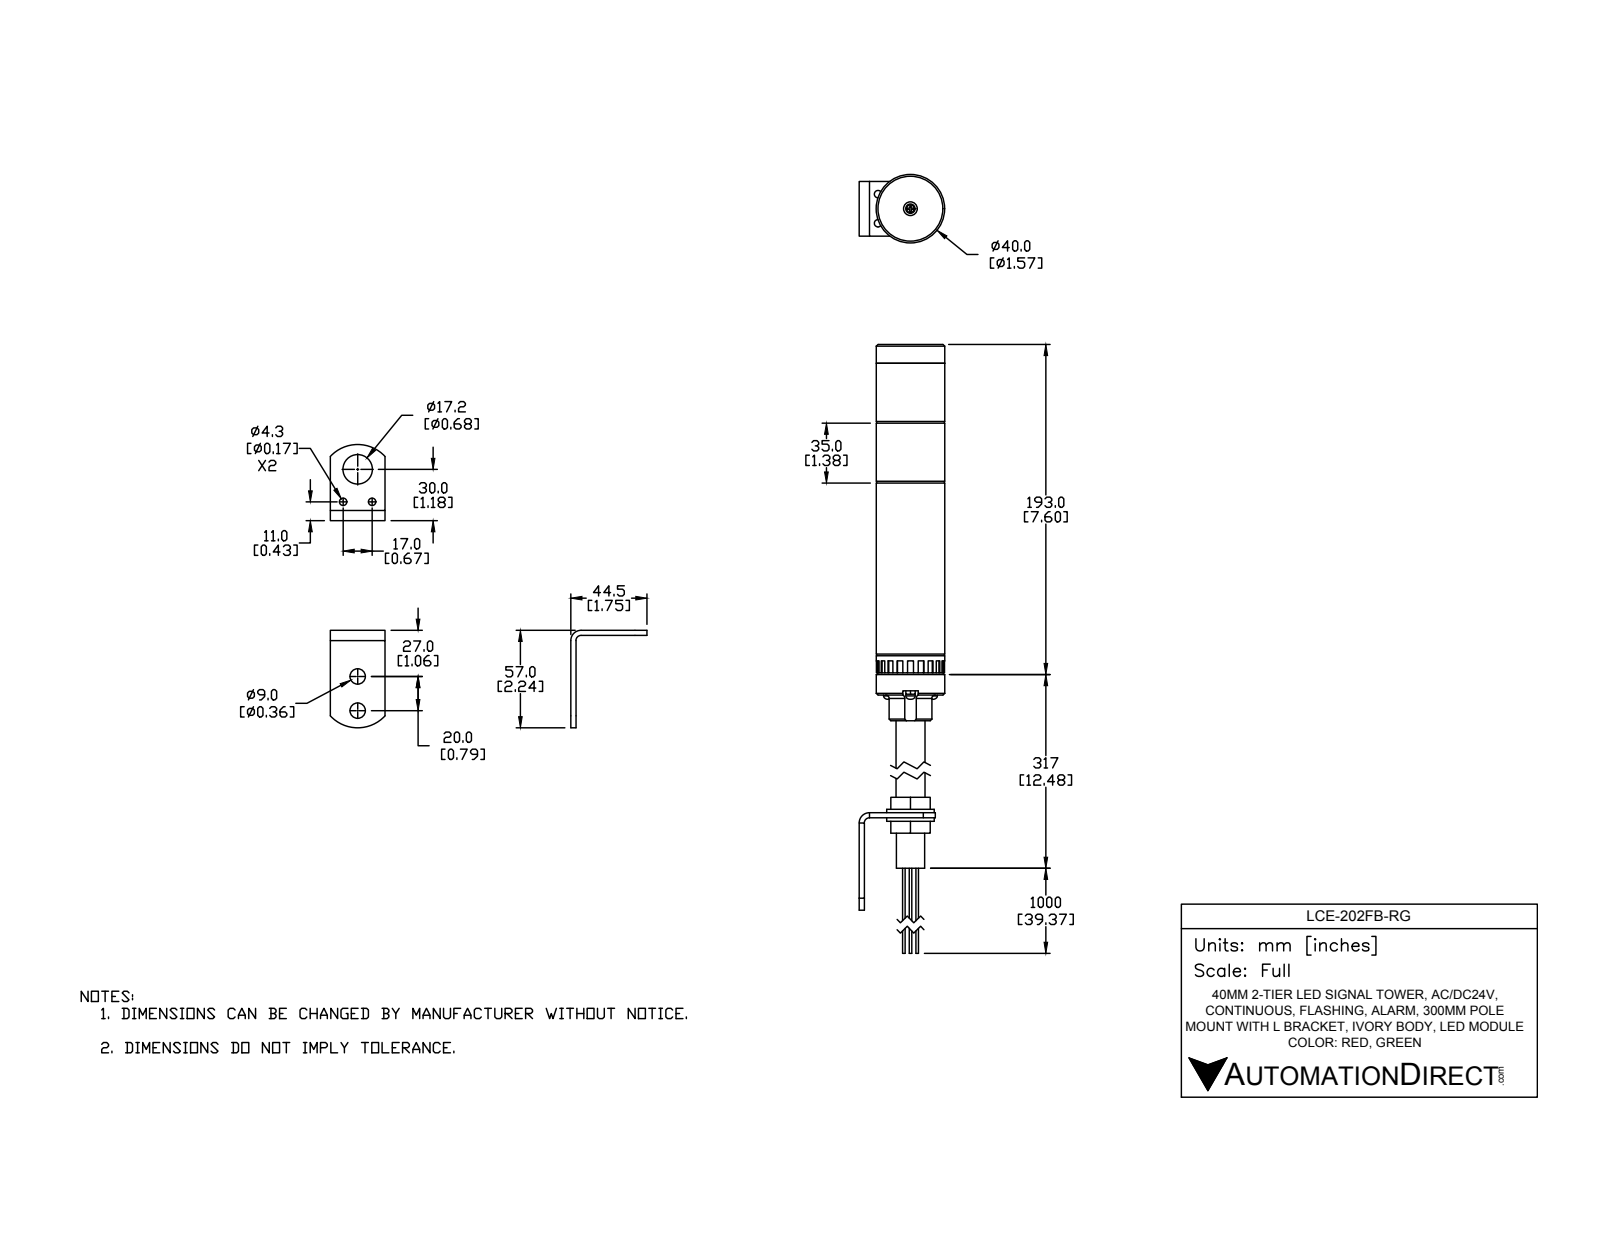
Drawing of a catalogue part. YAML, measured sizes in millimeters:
part_name: "LCE-202FB-RG"
step_written_by: "SolidWorks 2016 (AUTOMOTIVE_DESIGN)"
units: millimeters
bodies: {solids: 33, faces: 377, planar: 241, cylindrical: 116, other: 20}
overall_size: [593, 50, 40]
volume: 310333
surface_area: 112790
round_holes:
  - {diameter: 3.5, count: 3}
  - {diameter: 4, count: 3}
  - {diameter: 4.3, count: 2}
  - {diameter: 9.04, count: 2}
  - {diameter: 8, count: 1}
  - {diameter: 12, count: 1}
  - {diameter: 17.2, count: 1}
  - {diameter: 17.5, count: 1}
  - {diameter: 18, count: 1}
round_bosses_or_shafts:
  - {diameter: 1.5, count: 10}
  - {diameter: 5.5, count: 4}
  - {diameter: 3, count: 3}
  - {diameter: 40, count: 1}
  - {diameter: 39.5, count: 1}
  - {diameter: 38.5, count: 1}
  - {diameter: 27.8, count: 1}
  - {diameter: 17, count: 1}
partial_cylinders:
  - {radius: 4.5, count: 3}
  - {radius: 21.79, count: 2}
  - {radius: 3, count: 1}
  - {radius: 6, count: 1}
  - {radius: 12.5, count: 1}
face_to_face_distances: [1, 35, 11, 34, 101, 136, 112, 147, 182, 181]
hole_center_spacings: [15, 25.98, 20.81, 6.09, 17, 17.09, 20, 20.08]
